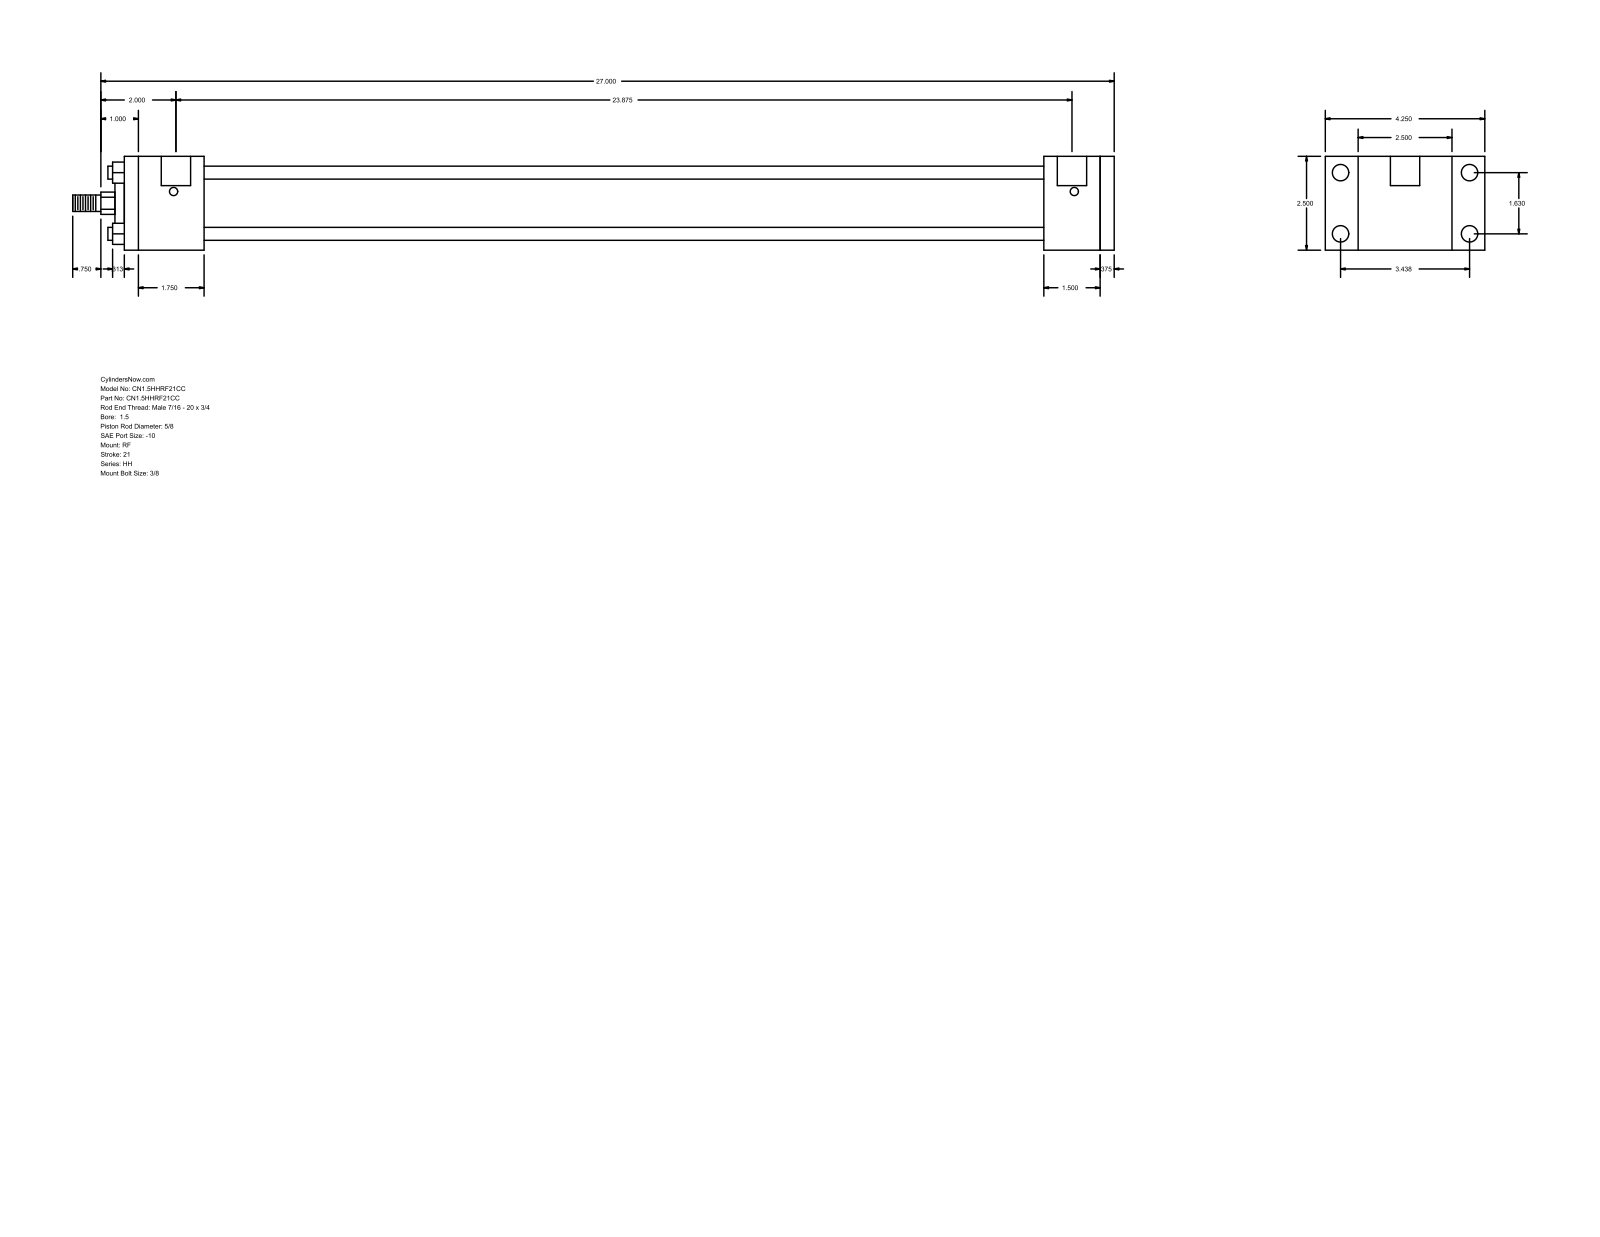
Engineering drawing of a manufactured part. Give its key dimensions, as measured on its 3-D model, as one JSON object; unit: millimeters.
{"part_name": "HH_RF__0150_0.625", "step_written_by": "GSSL Pune (CONFIG_CONTROL_DESIGN)", "units": "millimeters", "bodies": {"solids": 0, "faces": 92, "planar": 64, "cylindrical": 28, "other": 0}, "overall_size": [704.85, 107.95, 63.5], "round_holes": [[5.56, 4], [11.13, 4], [19.84, 2]], "round_bosses_or_shafts": [[8.76, 4], [44.45, 1], [28.57, 1], [15.88, 1], [11.11, 1]], "partial_cylinders_radius": [[7.54, 1]], "face_to_face_distances": [63.5, 669.92, 9.53, 38.1, 660.39, 47.63, 53.97, 622.29, 568.32, 606.42], "hole_center_spacings": [41.4, 87.32, 96.64, 609.6, 1.58, 1.59, 606.43, 608.01]}
